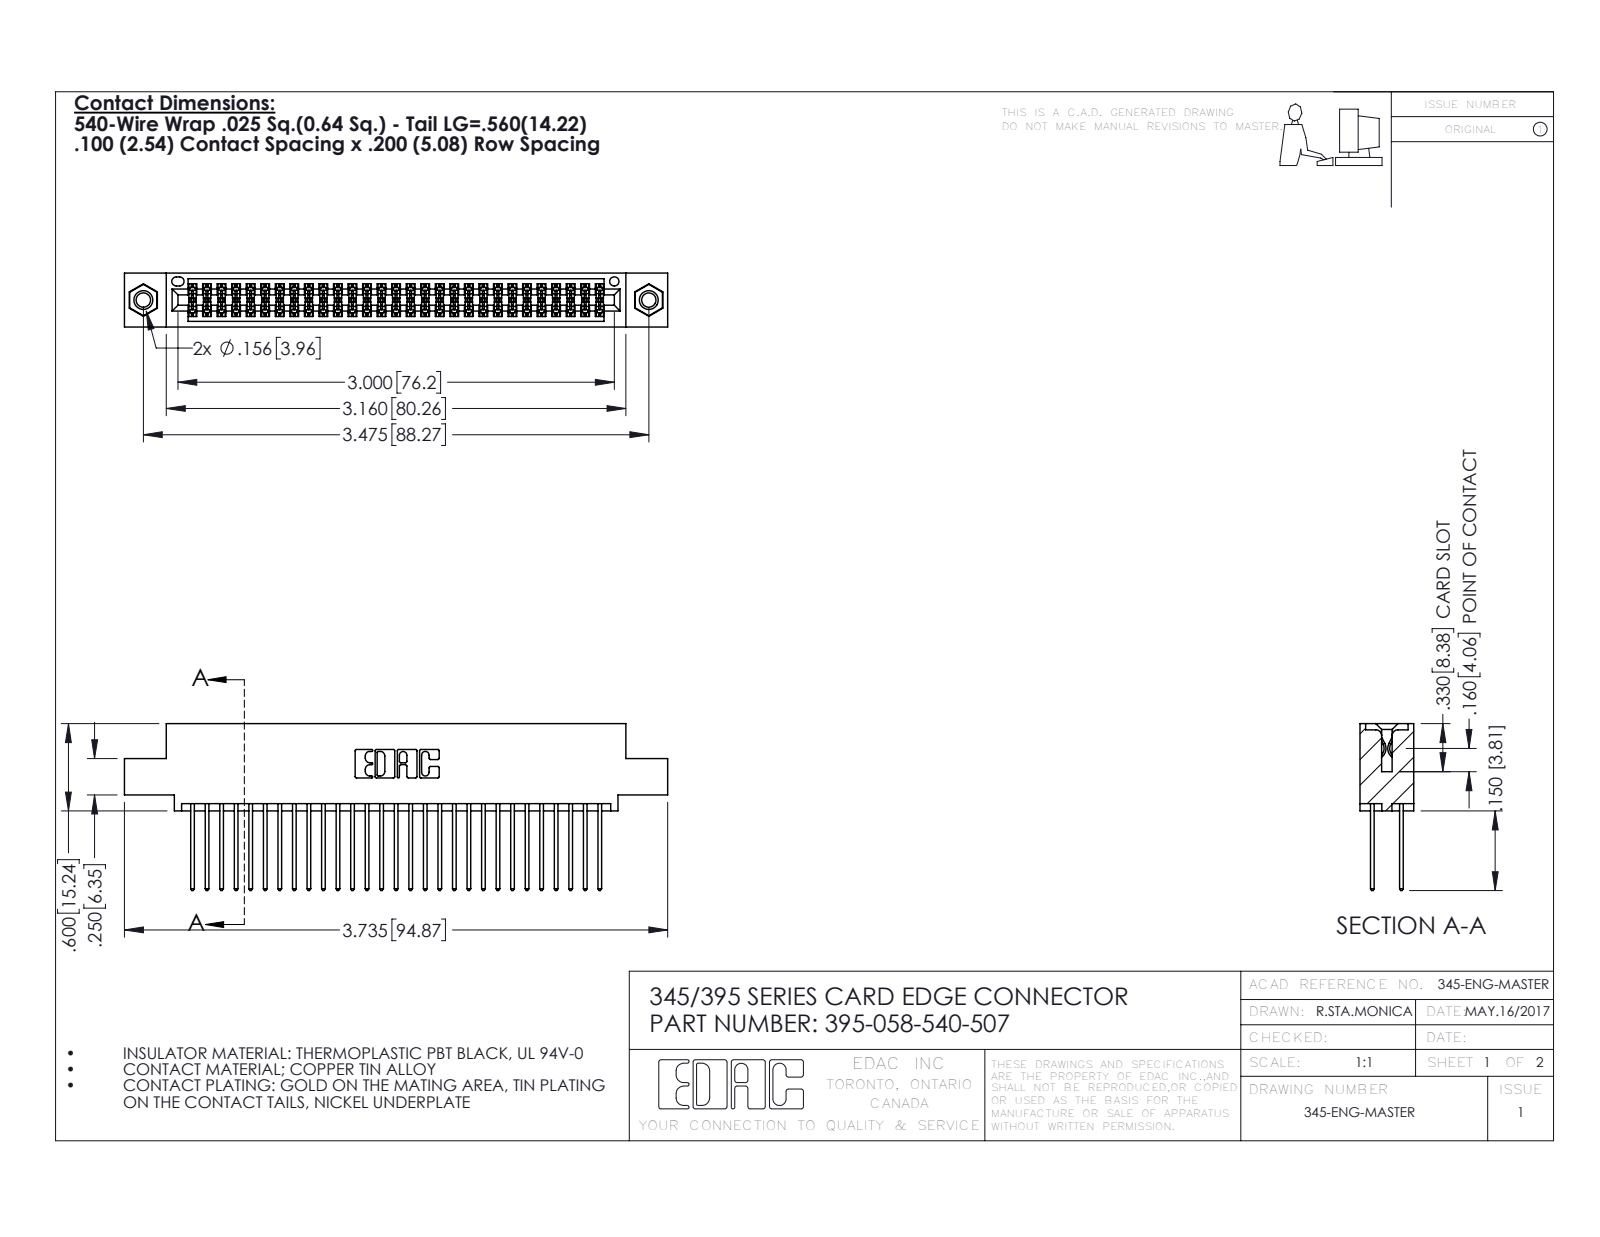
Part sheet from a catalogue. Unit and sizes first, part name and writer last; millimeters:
Units: millimetres
Overall size (bounding box): 94.9 × 29.1 × 9.4
Round holes (diameter × count): ⌀2.5 ×2, ⌀3.2 ×2, ⌀4 ×2, ⌀1.6 ×1
Round bosses / shafts (diameter × count): ⌀3.9 ×2
Partial cylindrical surfaces — rounded edges, fillets, slot ends (radius × count): R0.2 ×87, R0.3 ×58, R0.3 ×22, R0.2 ×6, R0.8 ×6, R0.7 ×3, R0.4 ×2, R0.5 ×2
Main face-to-face distances: 1.8, 7.6, 5.1, 2.5, 6.9, 0.6, 9.4, 5.7, 4.4, 3.8
Hole centre spacings: 6.9, 82.3, 88.3
Volume: 9 230 mm³ · Surface area: 14 530 mm²
Bodies: 61 solids, 3090 faces (2030 planar, 1044 cylindrical, 16 other)
Part name (STEP PRODUCT): 345-250-001_345-250-005-103; 395-058-540-507; 345 Part_0.110 Offset - 0.156 Dia-TI; 345-292-001_345-293-140
STEP written by: SolidWorks 2016 (CONFIG_CONTROL_DESIGN)
